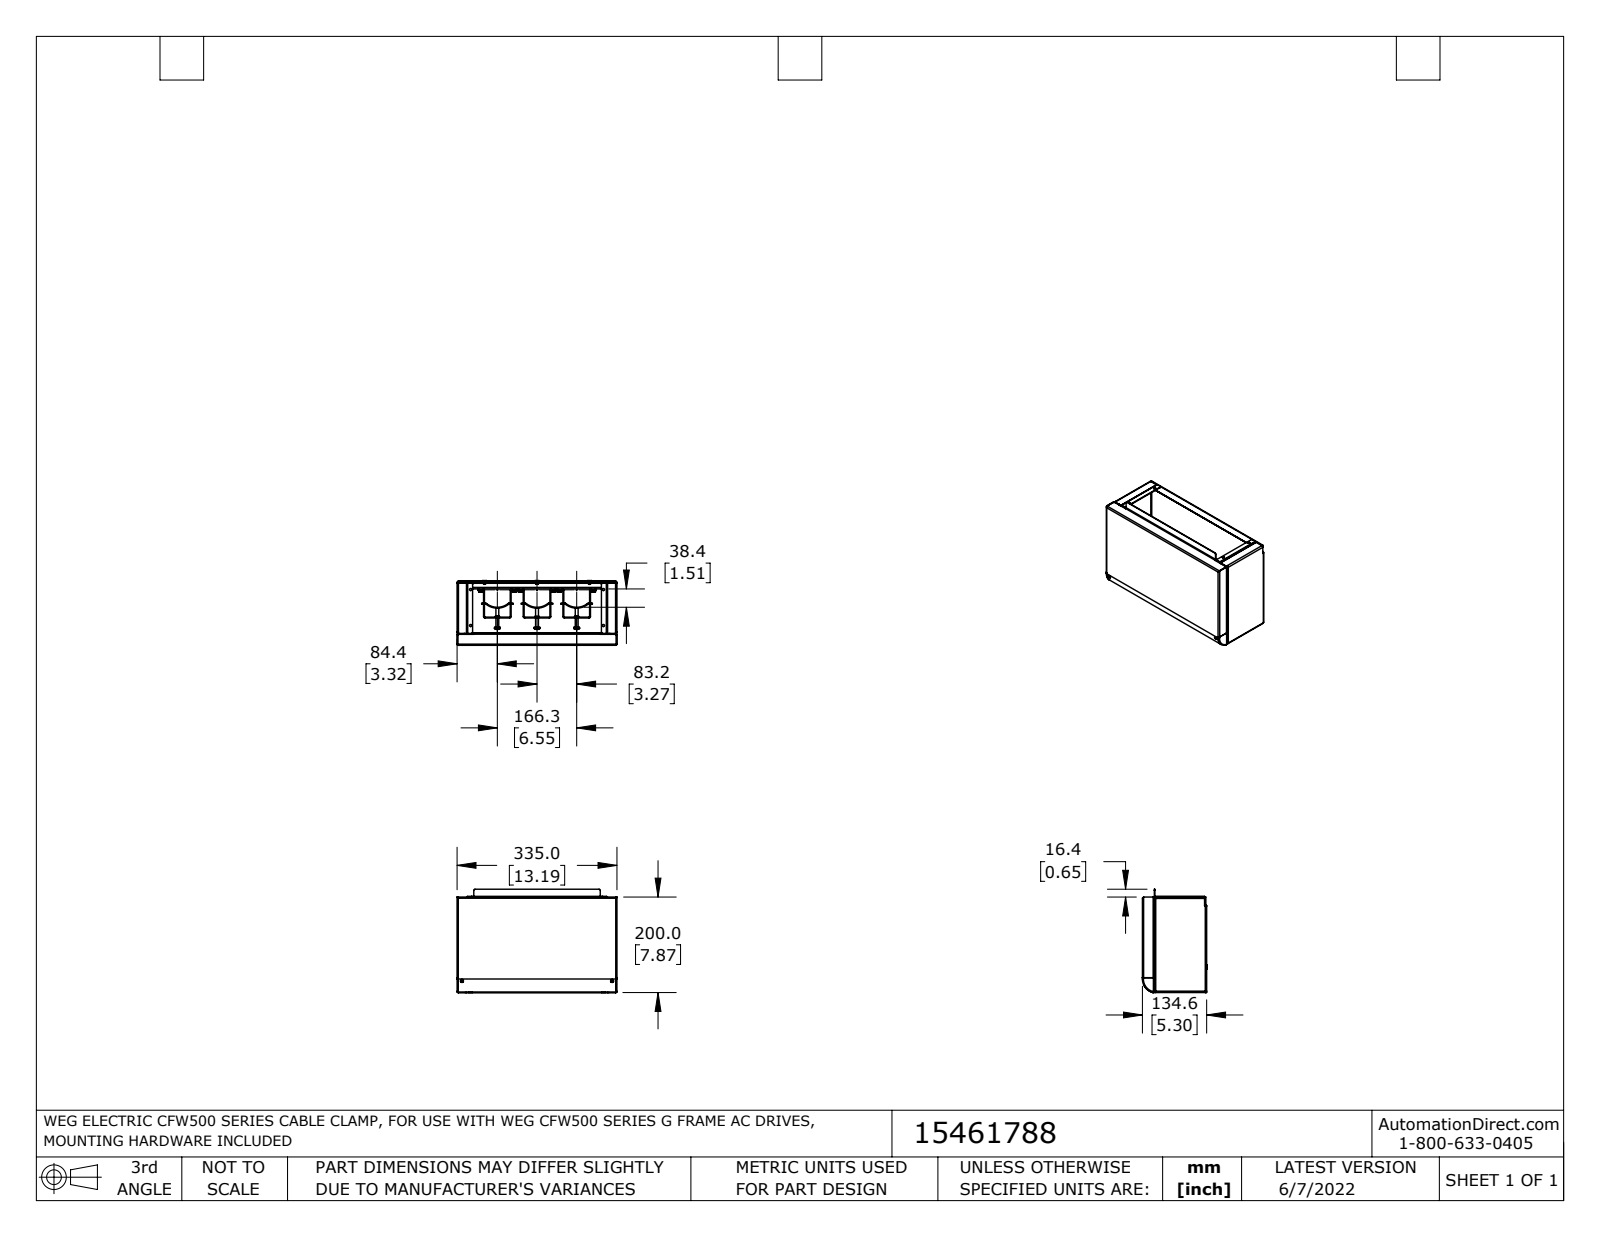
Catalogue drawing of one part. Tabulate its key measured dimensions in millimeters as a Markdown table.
| quantity | value |
| --- | --- |
| part name | 15461788_CFW500-KPCSG |
| STEP written by | SolidWorks 2021 (AUTOMOTIVE_DESIGN) |
| units | millimeters |
| bodies | 31 solids, 1545 faces (760 planar, 420 cylindrical, 365 other) |
| overall size | 335 × 216.4 × 135.7 |
| volume | 344 300 mm³ |
| surface area | 527 300 mm² |
| round holes (diameter × count) | 3.2 × 11, 5.5 × 9, 3.5 × 6, 3.7 × 6, 5.8 × 6, 4.5 × 4, 5 × 3, 2.5 × 2, 4.2 × 2, 5.2 × 2 |
| round bosses / shafts (diameter × count) | 6.2 × 11, 4 × 9, 8.4 × 7, 8.9 × 6, 6.6 × 6, 3.9 × 6, 3.3 × 6, 12 × 3 |
| partial cylindrical surfaces (radius × count) | 2.5 × 58, 3.1 × 16, 2 × 14, 1.2 × 12, 0.5 × 10, 1.4 × 8, 2.9 × 8, 1.5 × 6 |
| main face-to-face distances | 1.5, 1, 133.6, 132.1, 134.6, 133.1, 333.5, 24, 108.1, 335 |
| hole center spacings | 35.6, 83.2, 278.5, 314.6, 39.7, 47.6, 74.8, 110.1 |
